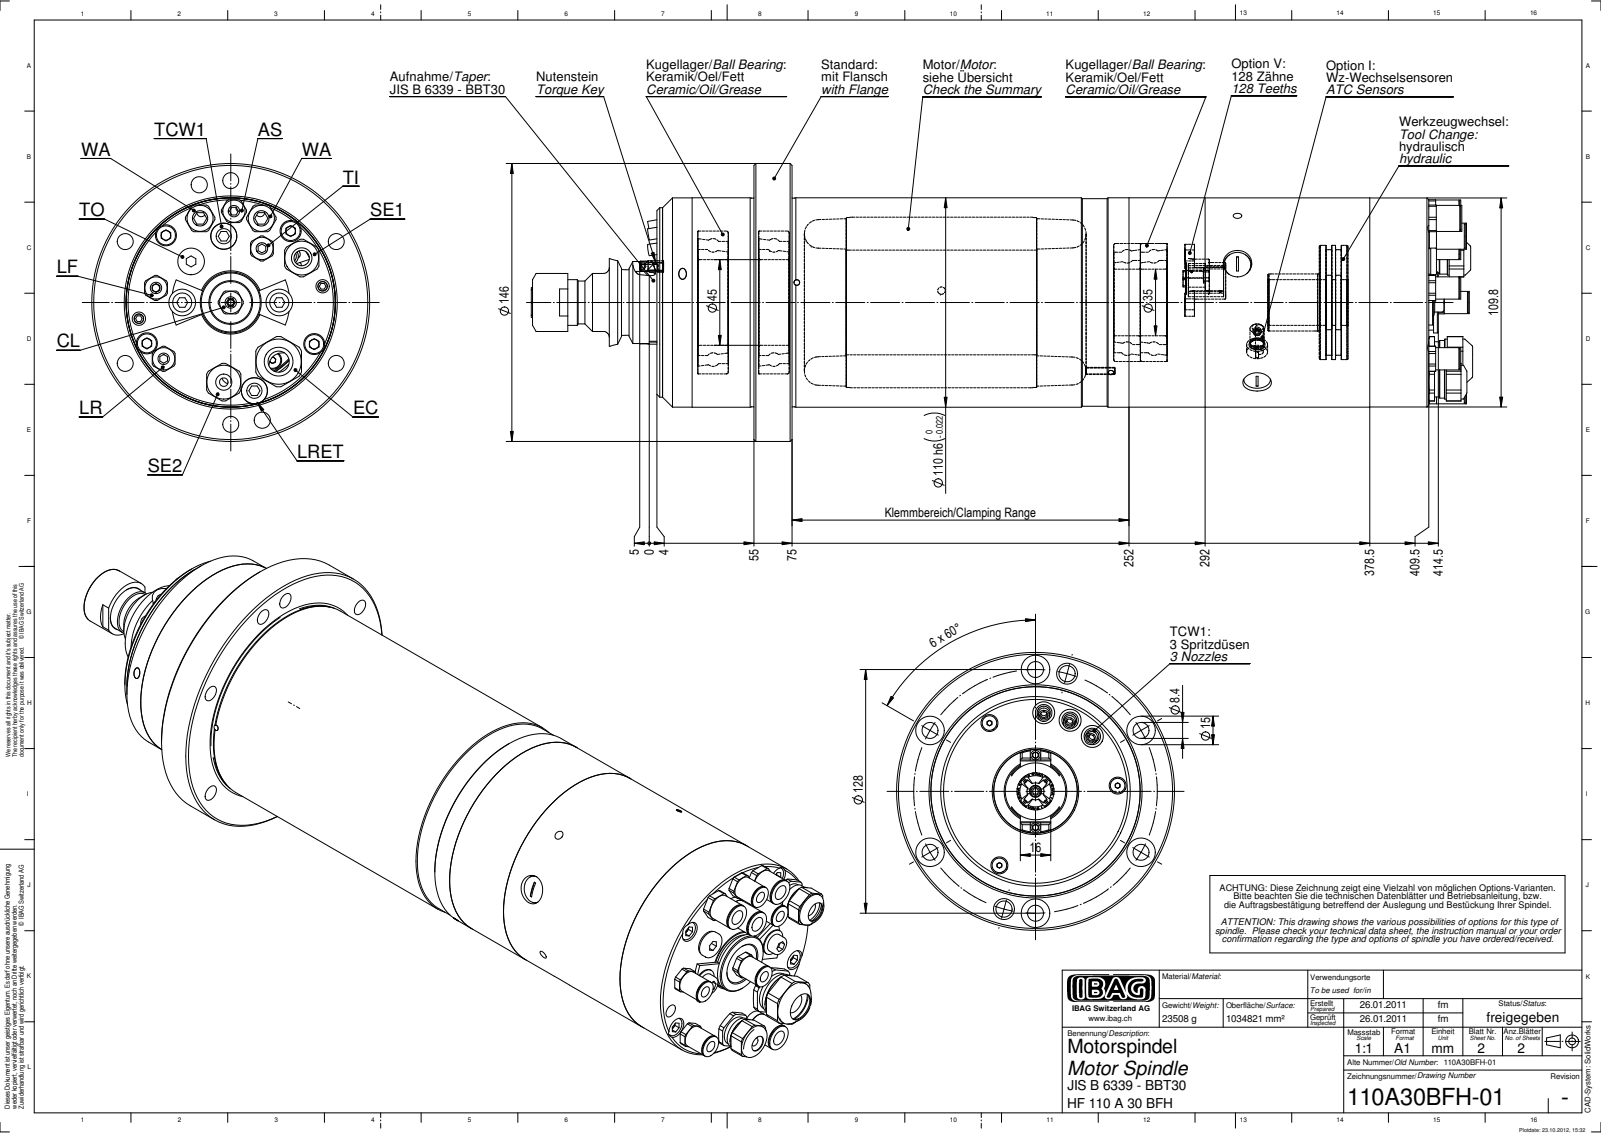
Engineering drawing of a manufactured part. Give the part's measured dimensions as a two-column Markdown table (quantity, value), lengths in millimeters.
| quantity | value |
| --- | --- |
| part name | 110A30BFH-01 |
| STEP written by | SolidWorks 2012 (CONFIG_CONTROL_DESIGN) |
| units | millimeters |
| bodies | 0 solids, 831 faces (317 planar, 353 cylindrical, 161 other) |
| overall size | 494.46 × 146 × 146 |
| round holes (diameter × count) | 15 × 9, 4.5 × 7, 11 × 7, 8.4 × 6, 6 × 5, 8 × 5, 8.5 × 3, 11.5 × 3, 7 × 2, 5 × 1, 6.8 × 1, 10 × 1 |
| round bosses / shafts (diameter × count) | 11.7 × 5, 14 × 4, 13.7 × 4, 7.64 × 3, 6 × 3, 17.8 × 2, 16.79 × 2, 15.59 × 2 |
| partial cylindrical surfaces (radius × count) | 6.6 × 5, 7.75 × 2, 9.9 × 2, 12.5 × 2, 6 × 1, 8.05 × 1, 13.2 × 1, 19 × 1 |
| main face-to-face distances | 387, 52.5, 334.5, 18.5, 71, 405.5, 51, 32.5, 20, 354.5 |
| hole center spacings | 64, 49, 110.85, 16.7, 24.56, 41.14, 41.5, 73.54 |
